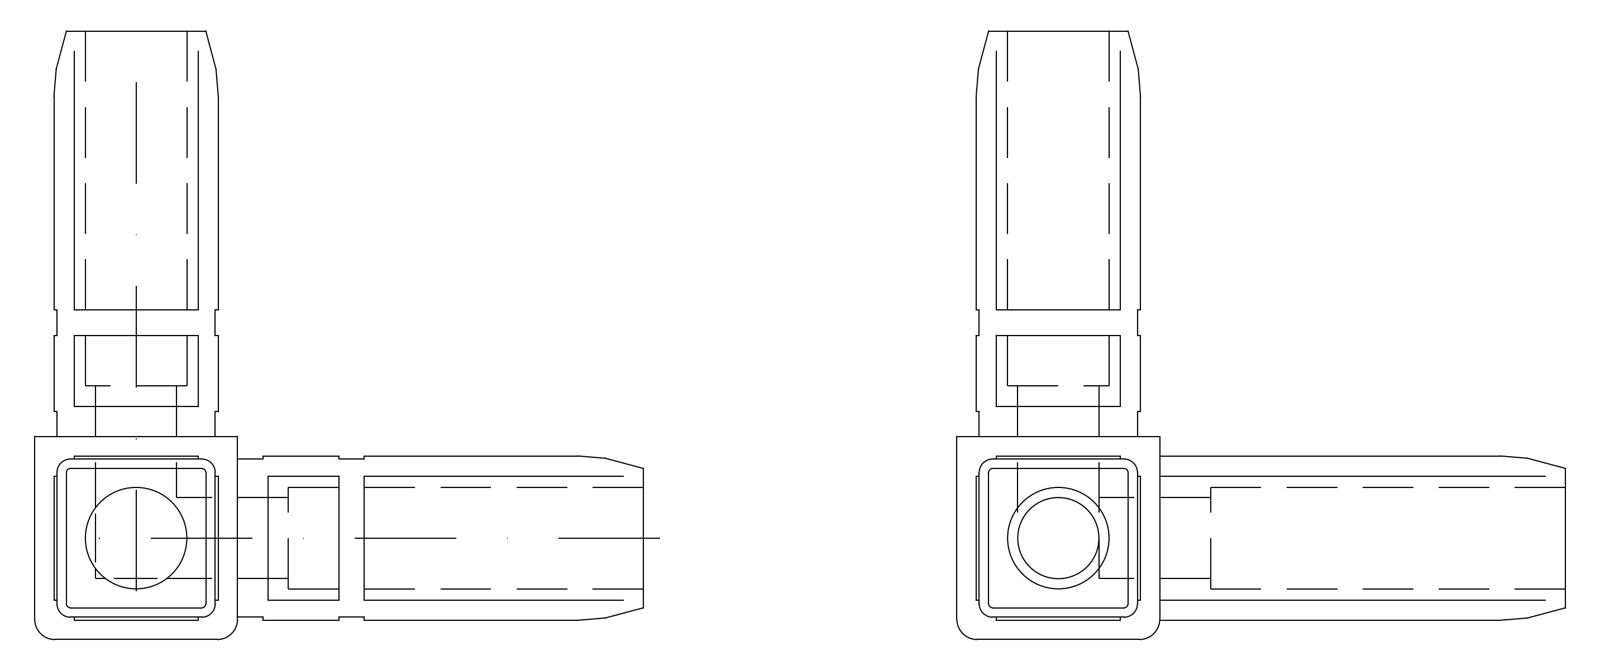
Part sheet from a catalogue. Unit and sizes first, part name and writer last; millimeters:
Units: millimetres
Overall size (bounding box): 60 × 60 × 60
Round holes (diameter × count): ⌀10 ×3
Partial cylindrical surfaces — rounded edges, fillets, slot ends (radius × count): R1.31 ×6, R1.33 ×4, R1 ×3, R1.31 ×2, R2 ×2
Main face-to-face distances: 16.2, 1.9, 18.1, 15.9, 17.8, 2.2, 20, 15.6, 60, 58.1
Volume: 28 578 mm³ · Surface area: 13 537 mm²
Bodies: 1 solid, 190 faces (144 planar, 20 cylindrical, 26 other)
STEP written by: THINKDESIGN (CONFIG_CONTROL_DESIGN)
